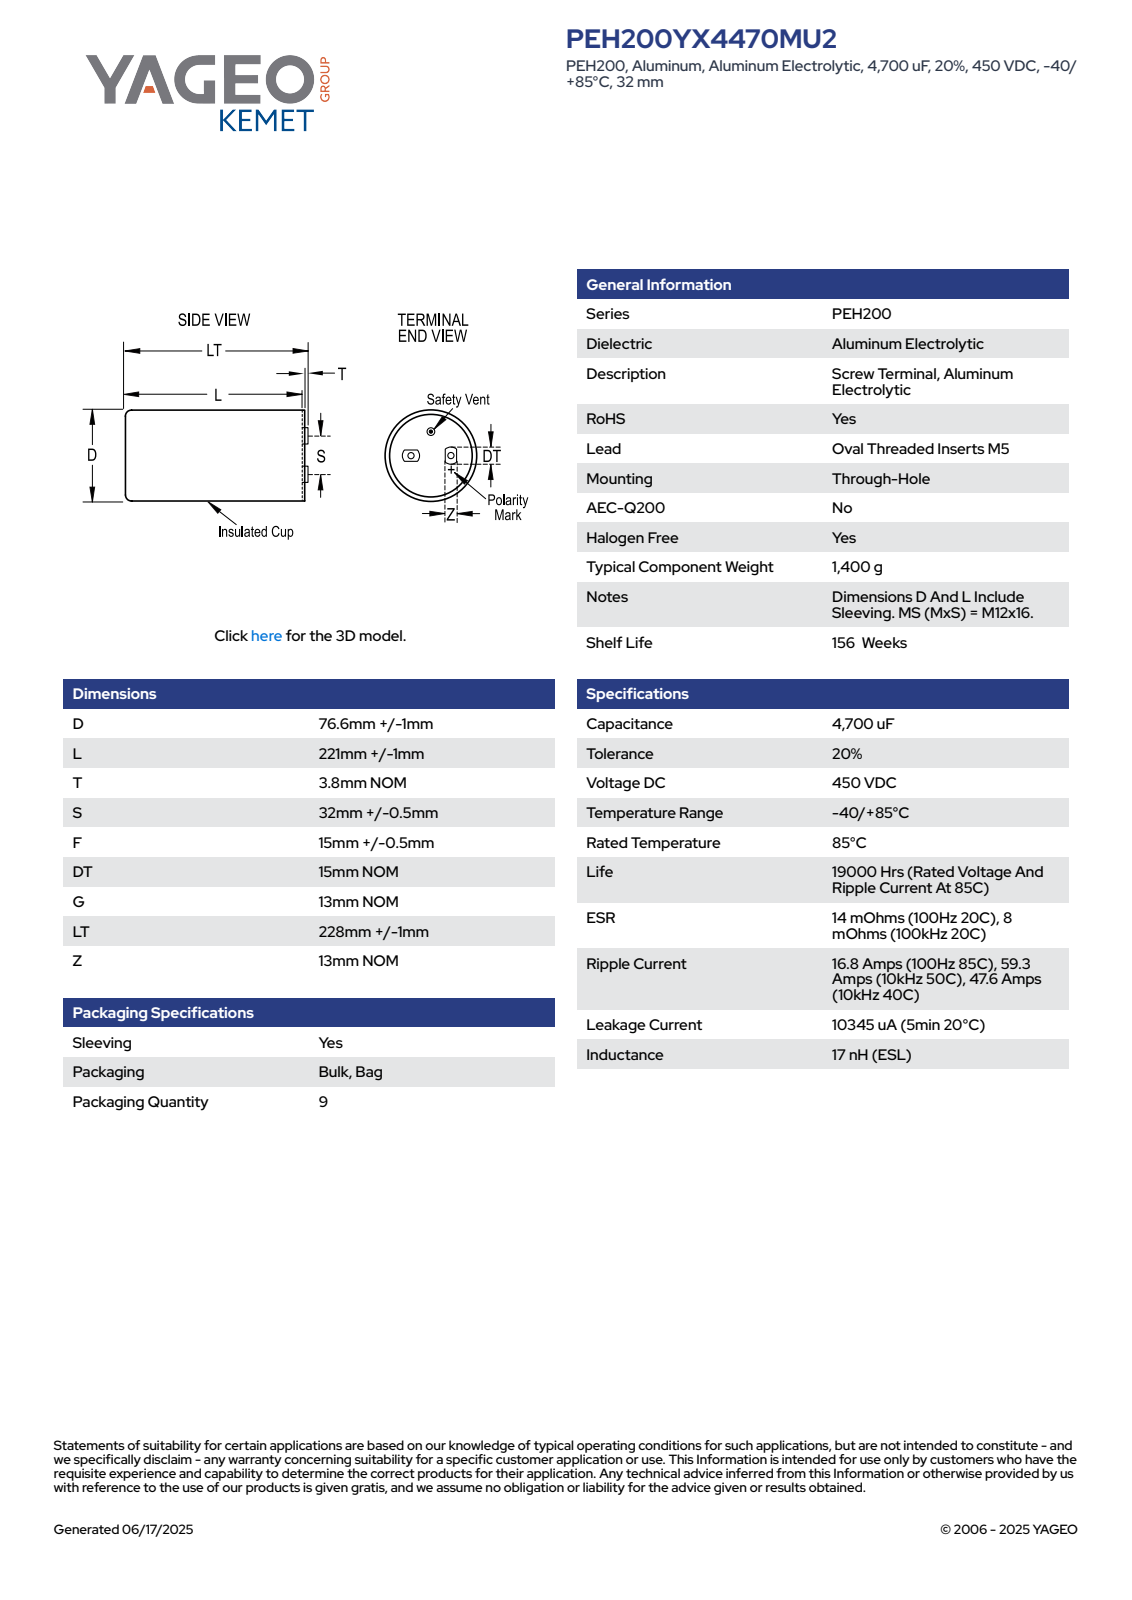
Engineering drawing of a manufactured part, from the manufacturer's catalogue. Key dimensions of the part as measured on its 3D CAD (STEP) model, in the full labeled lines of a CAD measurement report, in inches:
Part name (STEP PRODUCT): Oval_Terminal_8; CARC_D77.6L222S32T3.8; Can_8
STEP written by: SolidWorks 2014 (AUTOMOTIVE_DESIGN)
Units: inches
Bodies: 3 solids, 91 faces (38 planar, 21 cylindrical, 32 other)
Overall size (bounding box): 9.016 × 3.055 × 3.055
Volume: 64.2 in³ · Surface area: 103 in²
Round holes (diameter × count): ⌀0.158 ×2, ⌀2.976 ×1
Round bosses / shafts (diameter × count): ⌀0.295 ×2, ⌀3.055 ×1
Partial cylindrical surfaces — rounded edges, fillets, slot ends (radius × count): R0.295 ×2, R1.527 ×1
Main face-to-face distances: 8.74, 0.276, 9.016, 0.15, 0.126, 8.866, 0.512, 0.197, 0.472, 0.323
Hole centre spacings: 0.63, 1.26
